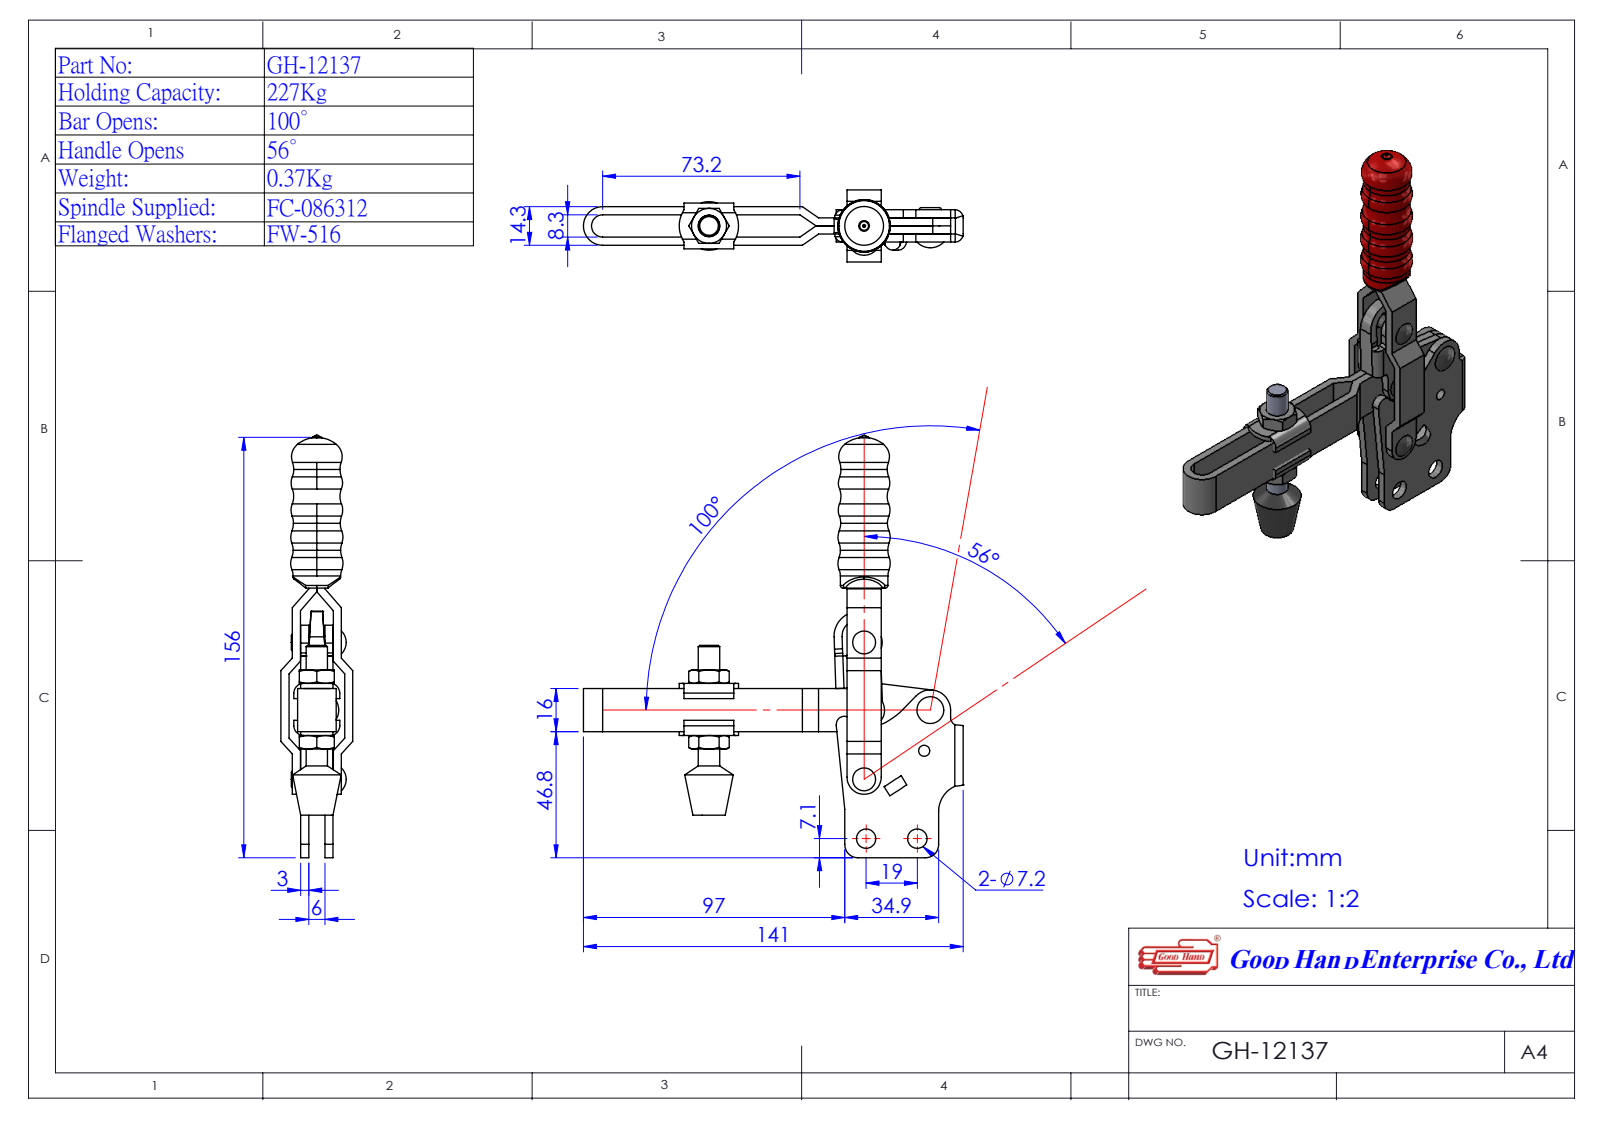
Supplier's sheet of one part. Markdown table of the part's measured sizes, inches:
| quantity | value |
| --- | --- |
| part name | GH-12137(簡化)-1; Group4^GH-12137(簡化)-1; Group2^GH-12137(簡化)-1; Group5^GH-12137(簡化)-1 (+2 more) |
| STEP written by | SolidWorks 2016 (AUTOMOTIVE_DESIGN) |
| units | inches |
| bodies | 5 solids, 338 faces (151 planar, 97 cylindrical, 90 other) |
| overall size | 6.148 × 5.551 × 1.051 |
| volume | 3.577 in³ |
| surface area | 55.62 in² |
| round holes (diameter × count) | 0.157 × 5, 0.283 × 2 |
| round bosses / shafts (diameter × count) | 0.693 × 1, 0.312 × 1, 0.248 × 1 |
| partial cylindrical surfaces (radius × count) | 0.059 × 4, 0.295 × 4, 0.004 × 2, 0.039 × 2, 0.079 × 2, 0.118 × 2, 0.122 × 2, 0.252 × 2 |
| main face-to-face distances | 0.118, 0.354, 0.045, 0.4, 0.236, 0.472, 0.518, 0.073, 0.163, 0.445 |
| hole center spacings | 0.601, 0.748, 0.867, 0.921, 0.972, 0.989, 1.013, 1.022 |
